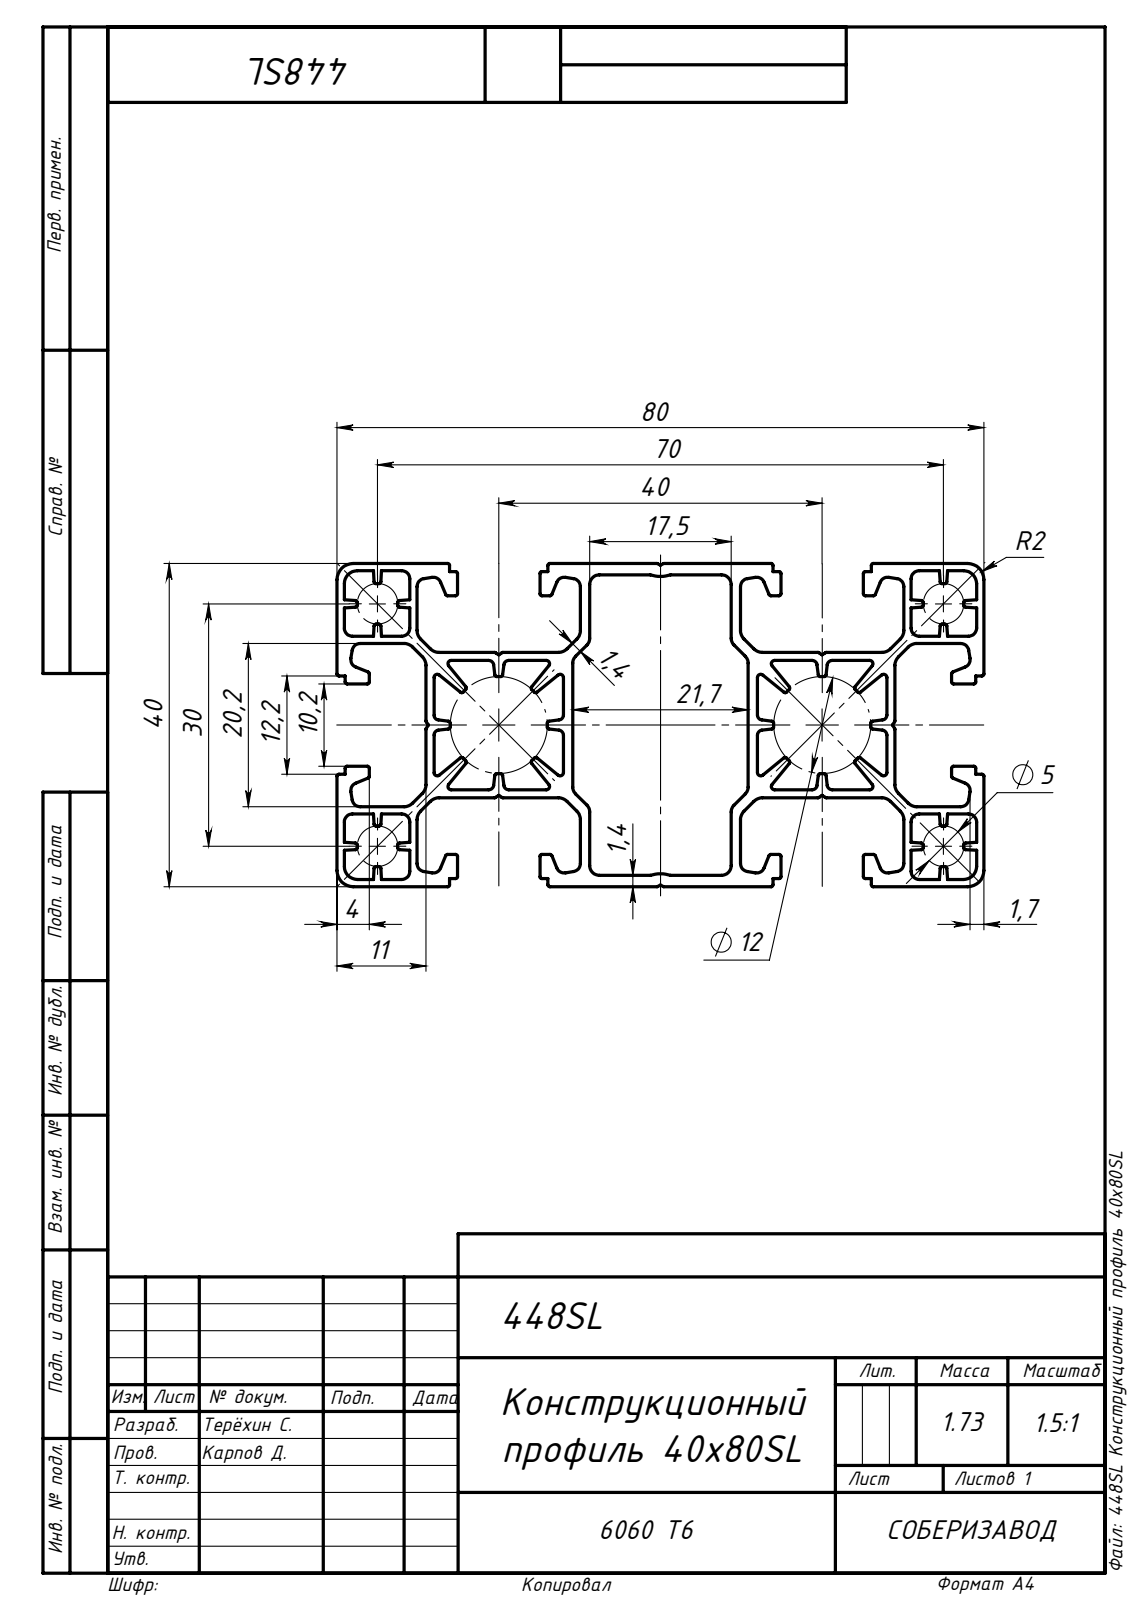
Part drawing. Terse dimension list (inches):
written by: SolidWorks 2019 (AUTOMOTIVE_DESIGN)
unit: in
bodies: 1 solid, 566 faces (296 planar, 270 cylindrical, 0 other)
size: 39.37 × 3.15 × 1.575
volume: 39.03 in³; area: 1 518 in²
rounds: 124× R0.01, 36× R0.039, 24× R0.059, 16× R0.016, 16× R0.024, 12× R0.047, 4× R0.063, 4× R0.079
face distances: 1.575, 0.433, 0.083, 0.354, 0.035, 0.039, 1.102, 1.185, 0.713, 0.472
